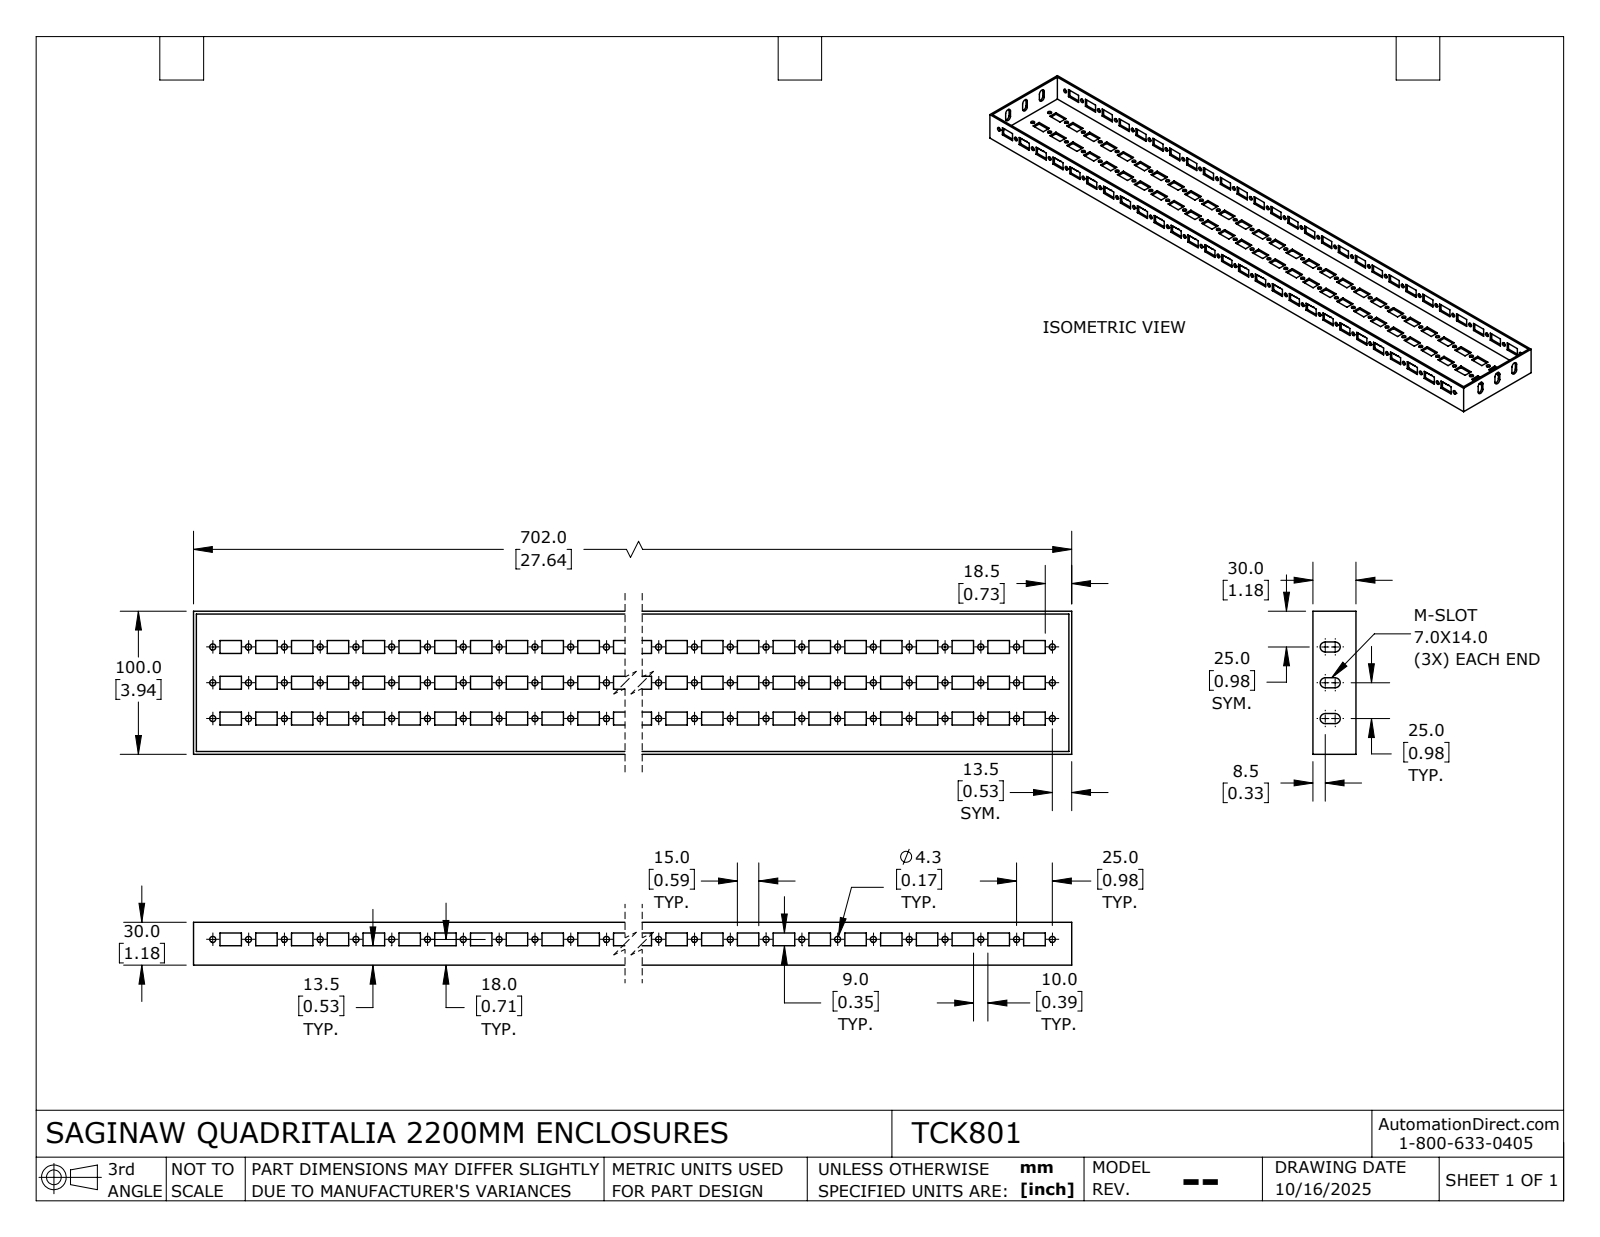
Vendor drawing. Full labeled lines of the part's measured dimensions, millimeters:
Part name (STEP PRODUCT): TCK801
STEP written by: SolidWorks 2024 (AUTOMOTIVE_DESIGN)
Units: millimetres
Bodies: 1 solid, 715 faces (563 planar, 152 cylindrical, 0 other)
Overall size (bounding box): 702 × 100 × 30
Volume: 188 304 mm³ · Surface area: 208 642 mm²
Round holes (diameter × count): ⌀4.25 ×112
Partial cylindrical surfaces — rounded edges, fillets, slot ends (radius × count): R3.5 ×6
Main face-to-face distances: 2, 98, 100, 96, 700, 25, 9, 20.5, 30, 28
Hole centre spacings: 25, 50, 55.9, 75, 100, 125, 35.36, 150
